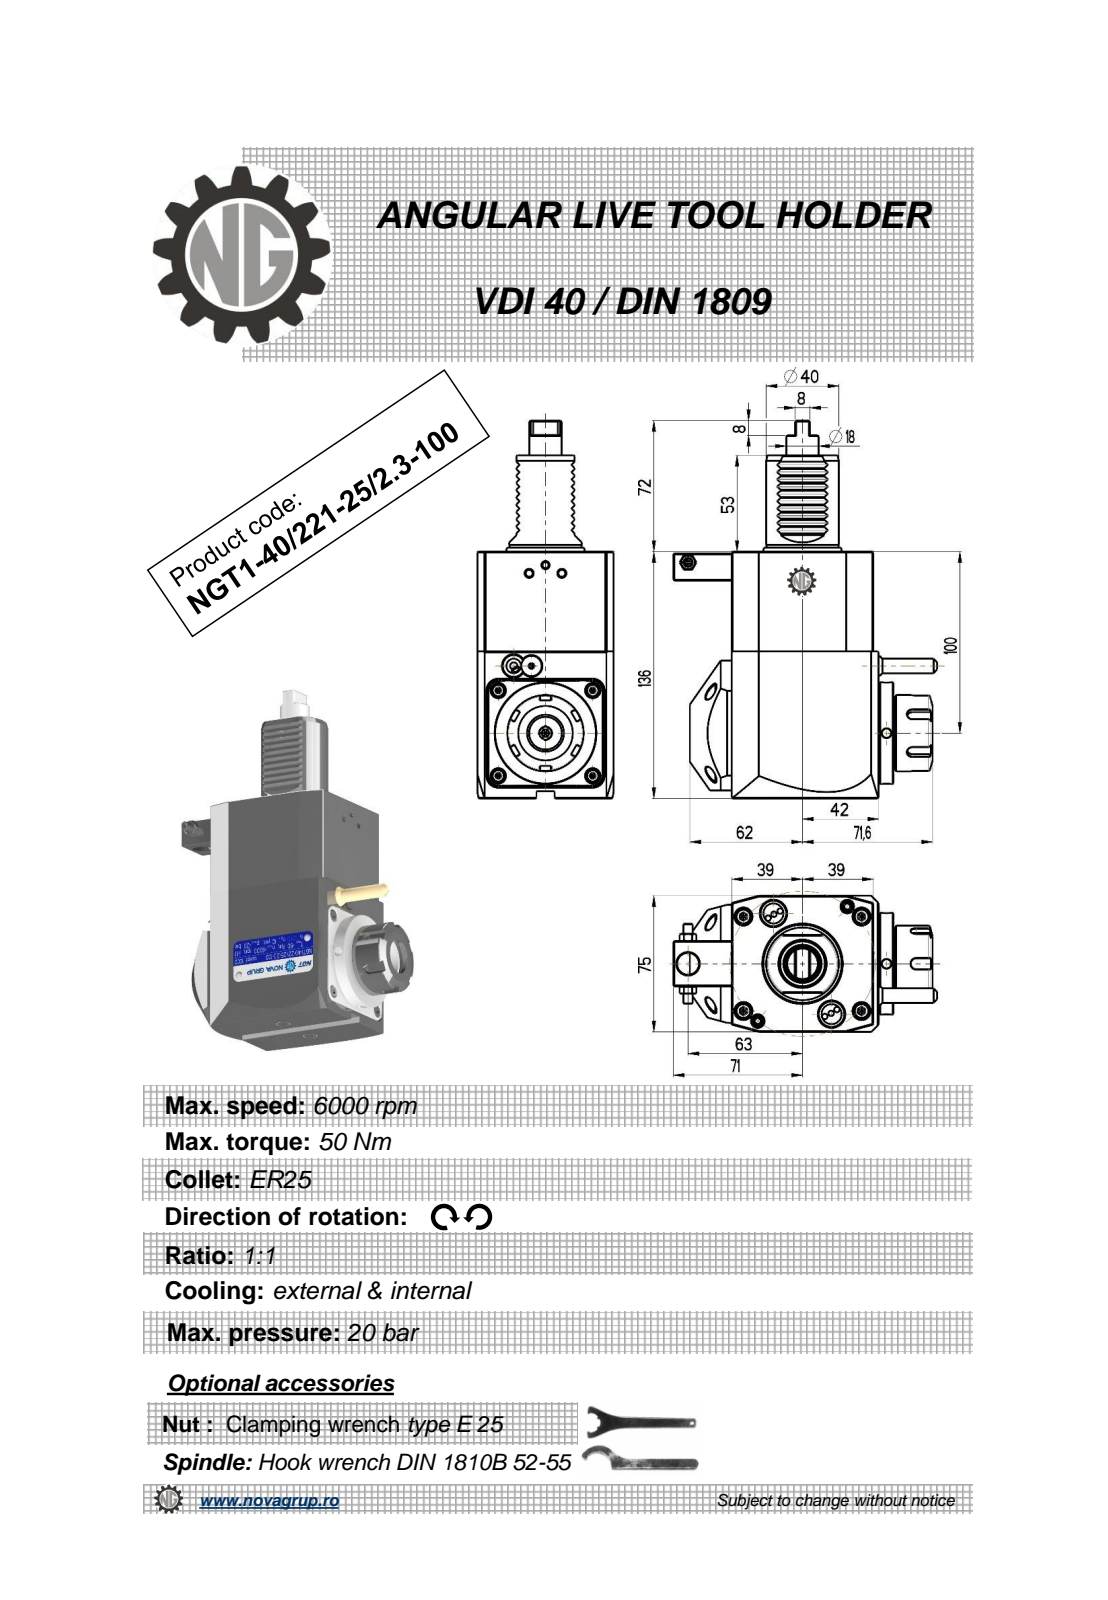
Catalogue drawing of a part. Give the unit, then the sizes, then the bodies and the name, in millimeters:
Units: millimetres
Overall size (bounding box): 208 × 145.14 × 75
Round holes (diameter × count): ⌀5 ×3, ⌀3 ×1, ⌀4.2 ×1, ⌀9.5 ×1, ⌀12 ×1, ⌀20.3 ×1
Round bosses / shafts (diameter × count): ⌀56 ×1, ⌀43 ×1, ⌀42 ×1, ⌀40 ×1, ⌀33 ×1, ⌀17.8 ×1, ⌀11.2 ×1, ⌀8.96 ×1
Partial cylindrical surfaces — rounded edges, fillets, slot ends (radius × count): R0.3 ×20, R0.26 ×12, R0.22 ×6, R3 ×5, R0.8 ×2, R40 ×1
Main face-to-face distances: 75, 136, 78, 81, 3, 11, 8, 84.88, 8.2, 80.8
Hole centre spacings: 40.93, 58.19, 92.5, 109.25, 144.12
Volume: 981 653 mm³ · Surface area: 76 496 mm²
Bodies: 1 solid, 467 faces (224 planar, 94 cylindrical, 149 other)
Part name (STEP PRODUCT): NGT1_40_221_25_2_3_100
STEP written by: PRO/ENGINEER BY PARAMETRIC TECHNOLOGY CORPORATION, 2010280 (CONFIG_CONTROL_DESIGN)
